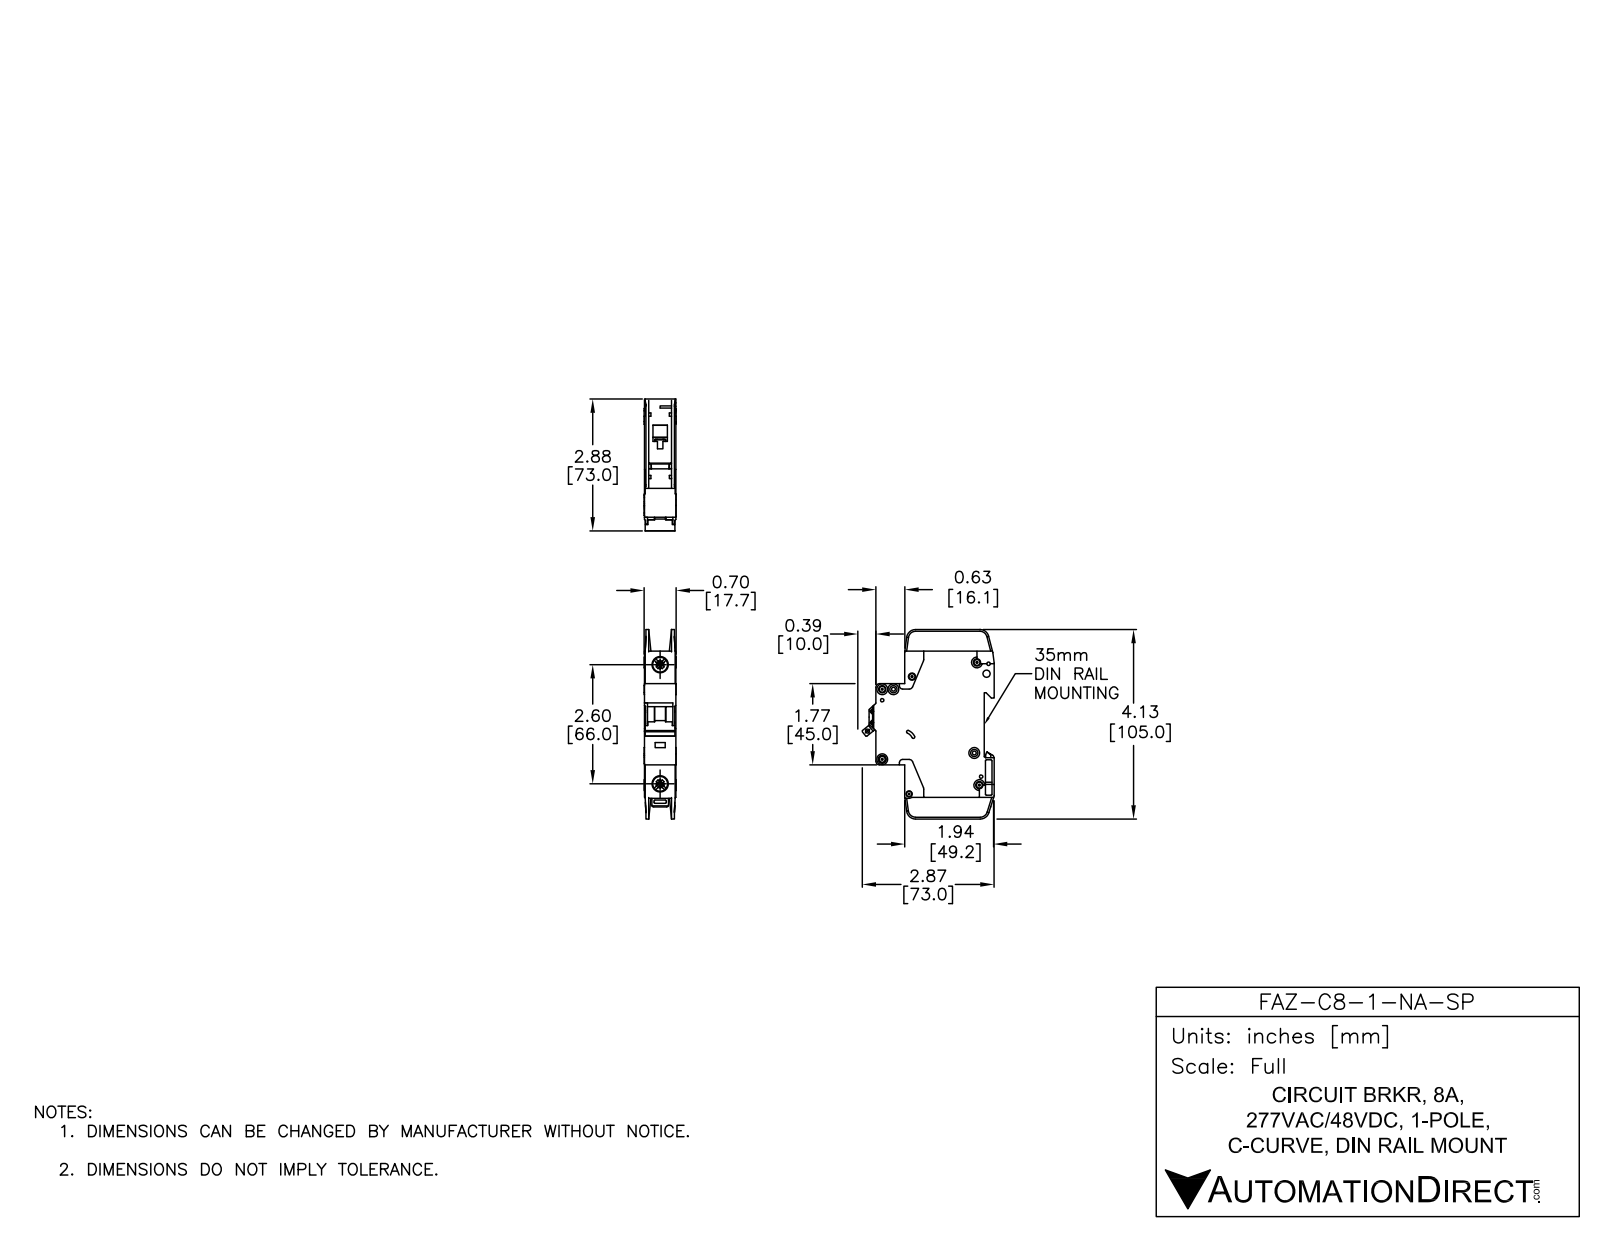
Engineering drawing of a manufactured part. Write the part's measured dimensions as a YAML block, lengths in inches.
part_name: "FAZ-C8-1-NA-SP"
step_written_by: "SolidWorks 2014 (AUTOMOTIVE_DESIGN)"
units: inches
bodies: {solids: 3, faces: 784, planar: 409, cylindrical: 263, other: 112}
overall_size: [4.134, 2.876, 0.697]
volume: 4.741
surface_area: 38.35
round_holes:
  - {diameter: 0.142, count: 7}
  - {diameter: 0.043, count: 2}
  - {diameter: 0.059, count: 2}
  - {diameter: 0.157, count: 2}
  - {diameter: 0.281, count: 2}
  - {diameter: 0.323, count: 2}
  - {diameter: 0.075, count: 1}
  - {diameter: 0.085, count: 1}
  - {diameter: 0.087, count: 1}
  - {diameter: 0.1, count: 1}
  - {diameter: 0.13, count: 1}
  - {diameter: 0.134, count: 1}
round_bosses_or_shafts:
  - {diameter: 0.236, count: 7}
  - {diameter: 0.098, count: 1}
partial_cylinders:
  - {radius: 0.01, count: 29}
  - {radius: 0.02, count: 18}
  - {radius: 0.039, count: 10}
  - {radius: 0.079, count: 10}
  - {radius: 0.197, count: 5}
  - {radius: 0.157, count: 4}
  - {radius: 0.071, count: 3}
  - {radius: 0.008, count: 2}
face_to_face_distances: [0.689, 0.593, 0.028, 0.096, 0.069, 0.62, 0.524, 0.551, 0.496, 0.079]
hole_center_spacings: [0.244, 0.204, 0.24, 0.322, 0.337, 0.343, 0.437, 0.49]
